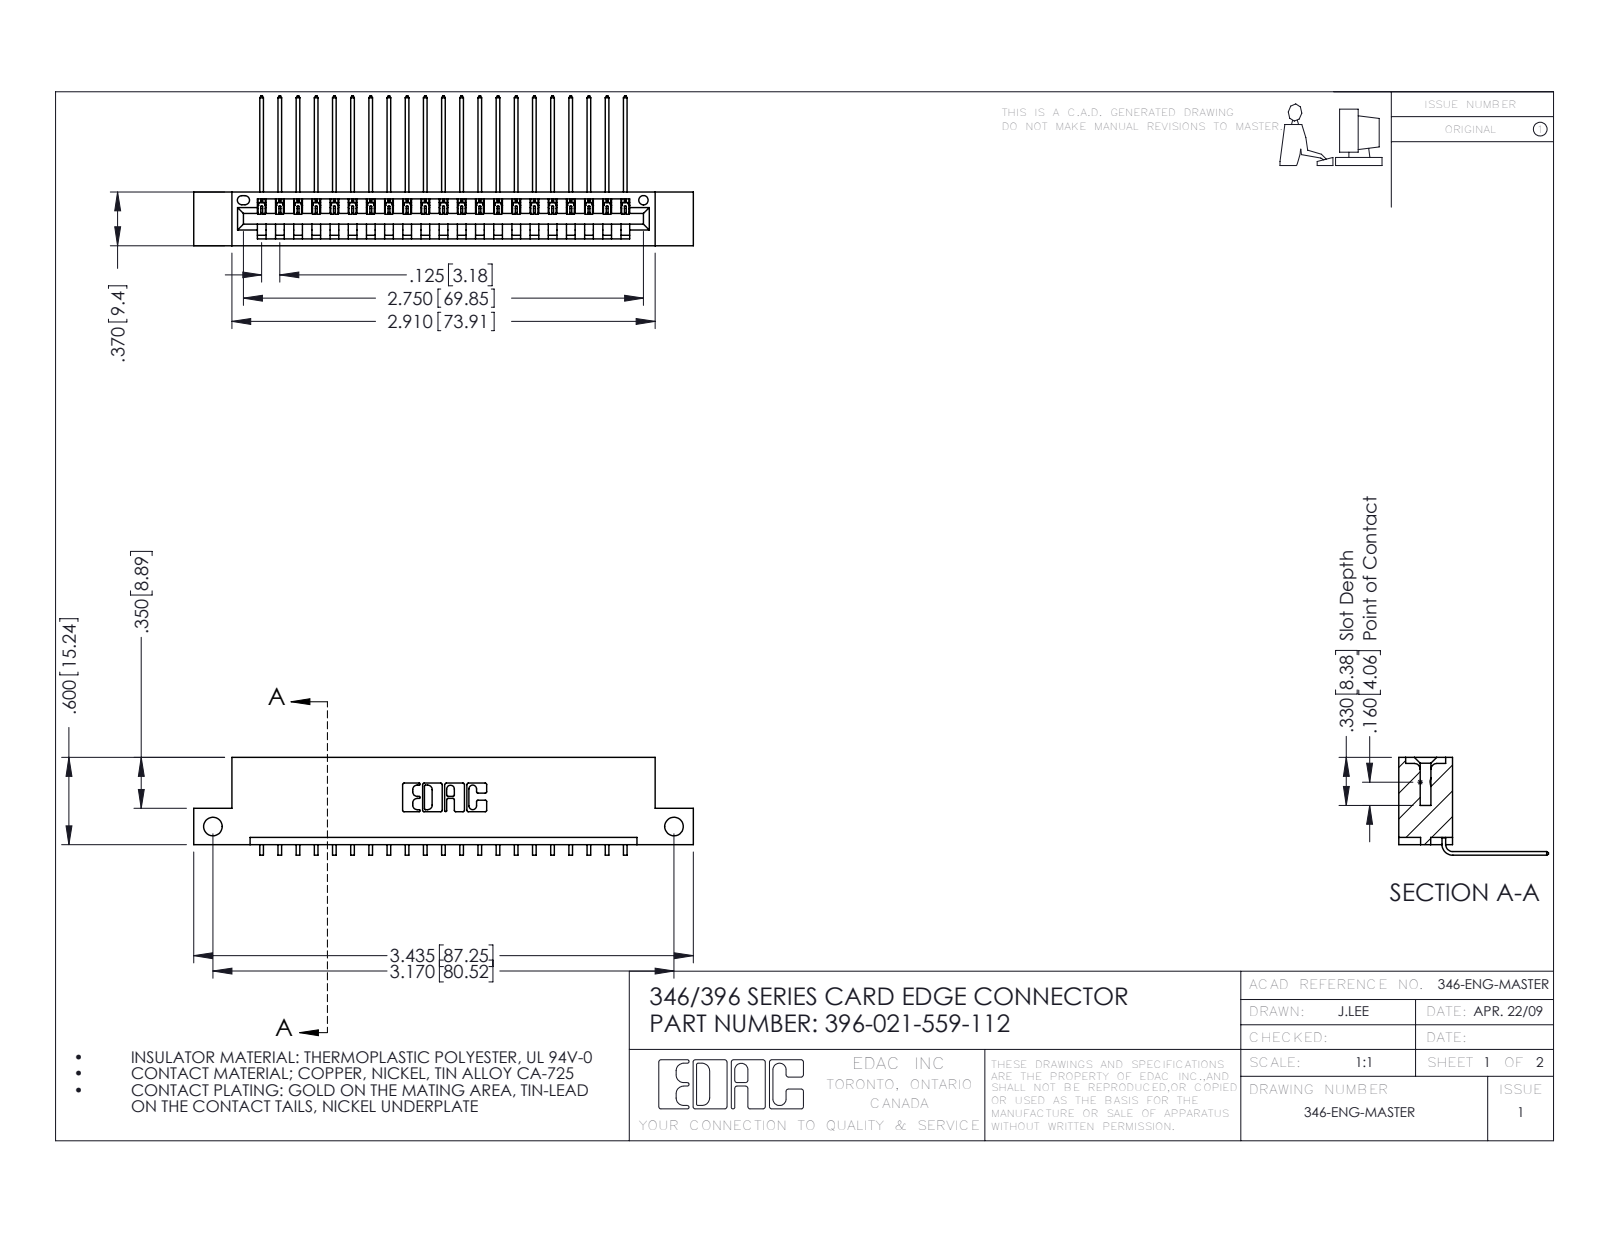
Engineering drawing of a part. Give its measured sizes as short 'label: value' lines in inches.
name: 346 Part_Flush Mounting Lugs - Side Mount; 396-021-559-112; 345-292-001_558 559 Tail - 1
written by: SolidWorks 2016 (CONFIG_CONTROL_DESIGN)
unit: in
bodies: 22 solids, 1382 faces (958 planar, 424 cylindrical, 0 other)
size: 3.435 × 1.03 × 0.673
volume: 0.5 in³; area: 15.94 in²
holes: 2× ⌀0.128, 1× ⌀0.064
rounds: 42× R0.006, 22× R0.01, 6× R0.007, 6× R0.031, 3× R0.026, 2× R0.031, 2× R0.04, 1× R0.014
face distances: 0.048, 0.322, 0.37, 0.25, 0.072, 0.025, 0.298, 0.148, 0.222, 0.1
hole spacings: 3.17
